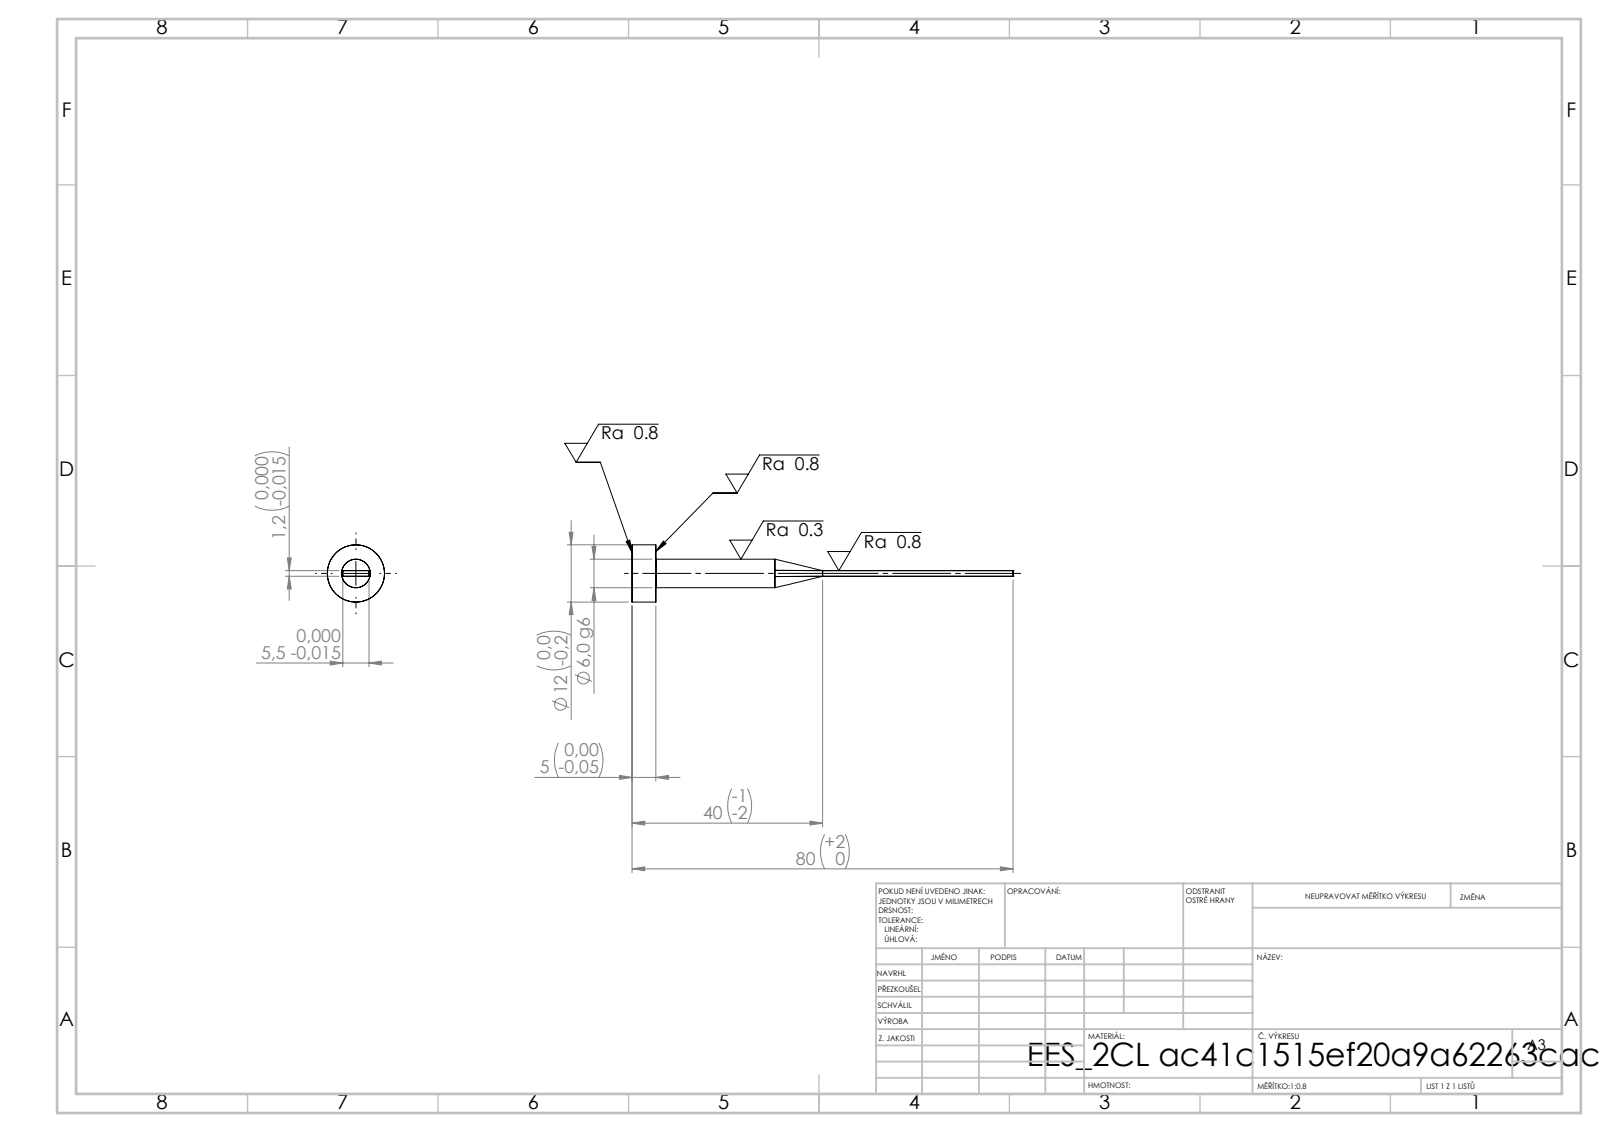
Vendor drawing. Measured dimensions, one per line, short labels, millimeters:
written by: SolidWorks 2019 (CONFIG_CONTROL_DESIGN)
unit: mm
bodies: 1 solid, 15 faces (7 planar, 4 cylindrical, 4 other)
size: 80 × 12 × 12
volume: 1 702 mm³; area: 1 557 mm²
bosses: 1× ⌀12, 1× ⌀6
face distances: 1.2, 5, 5.5, 80, 75
